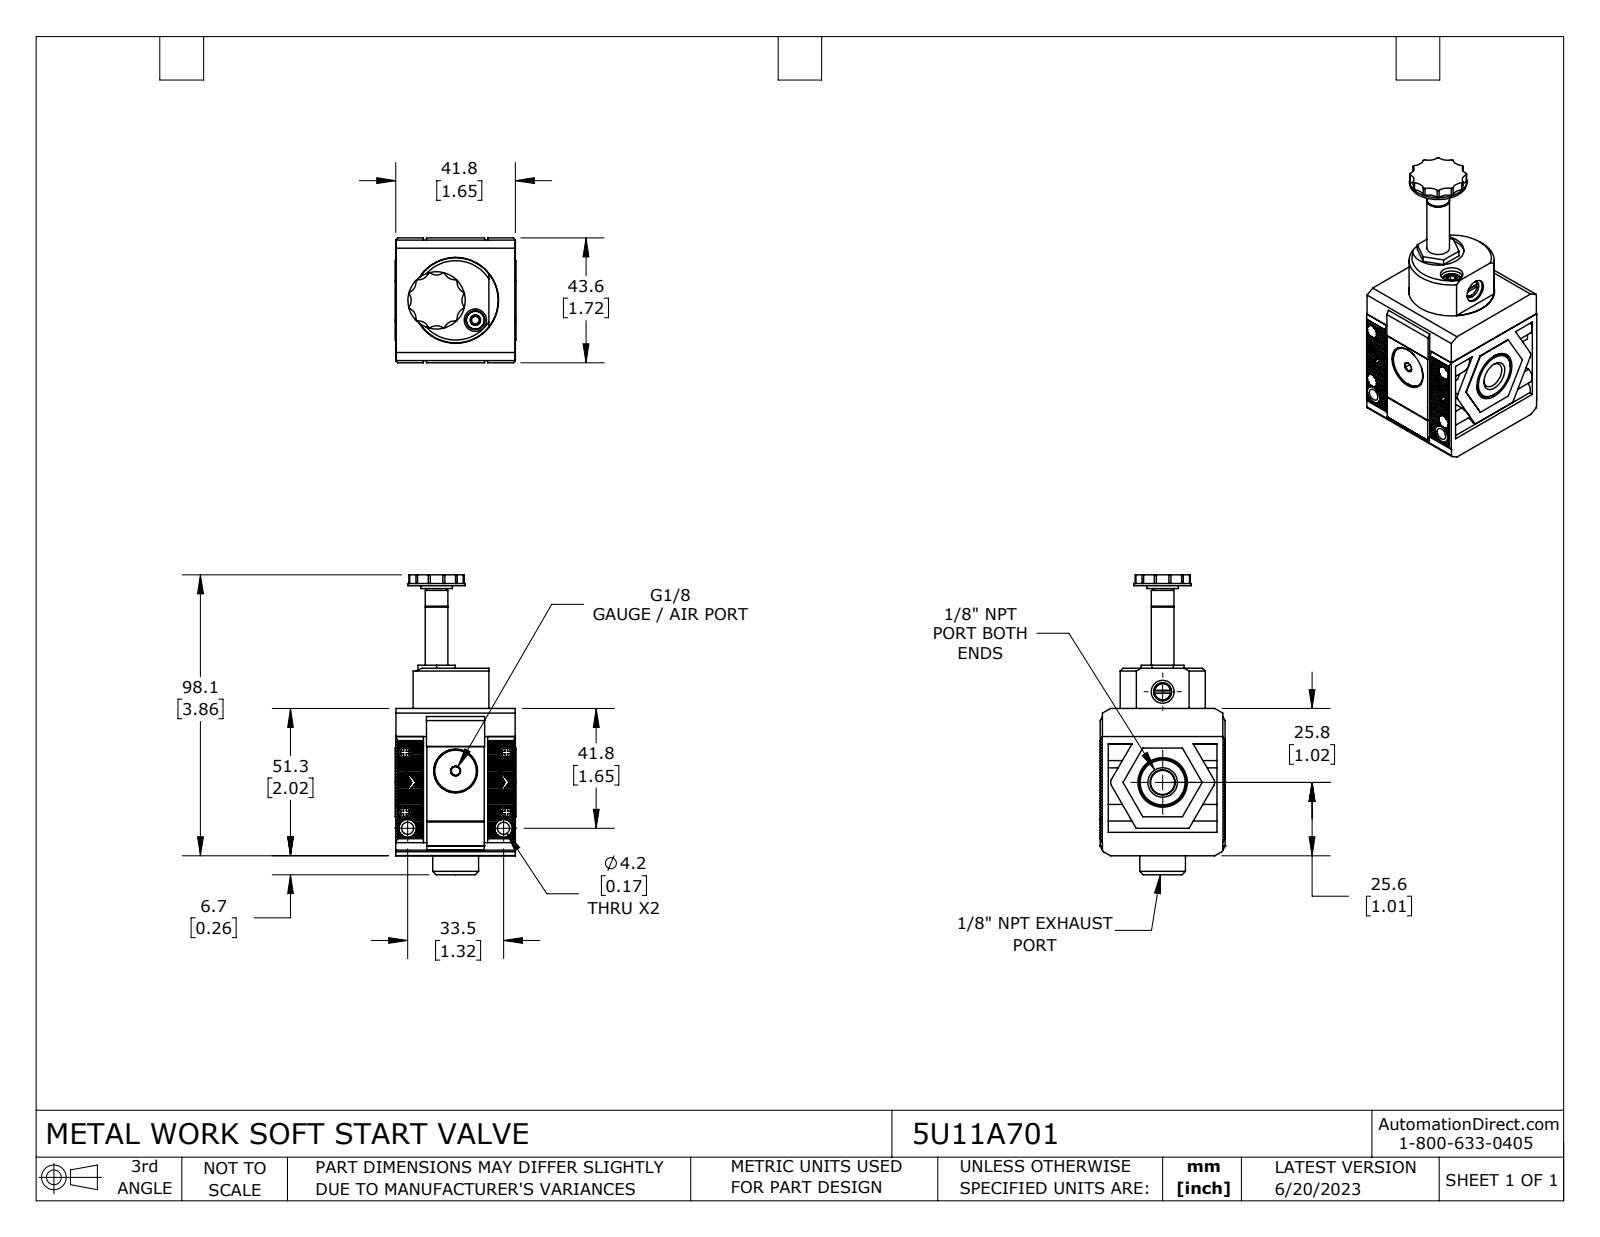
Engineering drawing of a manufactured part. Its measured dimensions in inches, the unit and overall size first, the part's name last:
Units: inches
Overall size (bounding box): 4.12 × 1.717 × 1.661
Round holes (diameter × count): ⌀0.083 ×4, ⌀0.118 ×4, ⌀0.185 ×4, ⌀0.165 ×2, ⌀0.337 ×2, ⌀0.248 ×1, ⌀0.256 ×1, ⌀0.307 ×1, ⌀0.315 ×1, ⌀0.602 ×1, ⌀1.181 ×1, ⌀1.26 ×1
Round bosses / shafts (diameter × count): ⌀0.181 ×4, ⌀0.102 ×4, ⌀0.244 ×2, ⌀1.169 ×1, ⌀0.898 ×1, ⌀0.787 ×1, ⌀0.717 ×1, ⌀0.63 ×1
Partial cylindrical surfaces — rounded edges, fillets, slot ends (radius × count): R0.02 ×12, R0.148 ×12, R0.024 ×4, R0.122 ×4, R0.008 ×2, R0.079 ×2, R0.354 ×1
Main face-to-face distances: 1.638, 1.339, 0.307, 1.642, 1.673, 1.654, 0.031, 0.071, 0.043, 0.315
Hole centre spacings: 0.222, 0.742, 0.823, 0.9, 1.027, 1.042, 1.374, 1.394
Volume: 6.081 in³ · Surface area: 55.45 in²
Bodies: 13 solids, 1206 faces (819 planar, 244 cylindrical, 143 other)
Part name (STEP PRODUCT): 5U11A701
STEP written by: SolidWorks 2021 (CONFIG_CONTROL_DESIGN)
